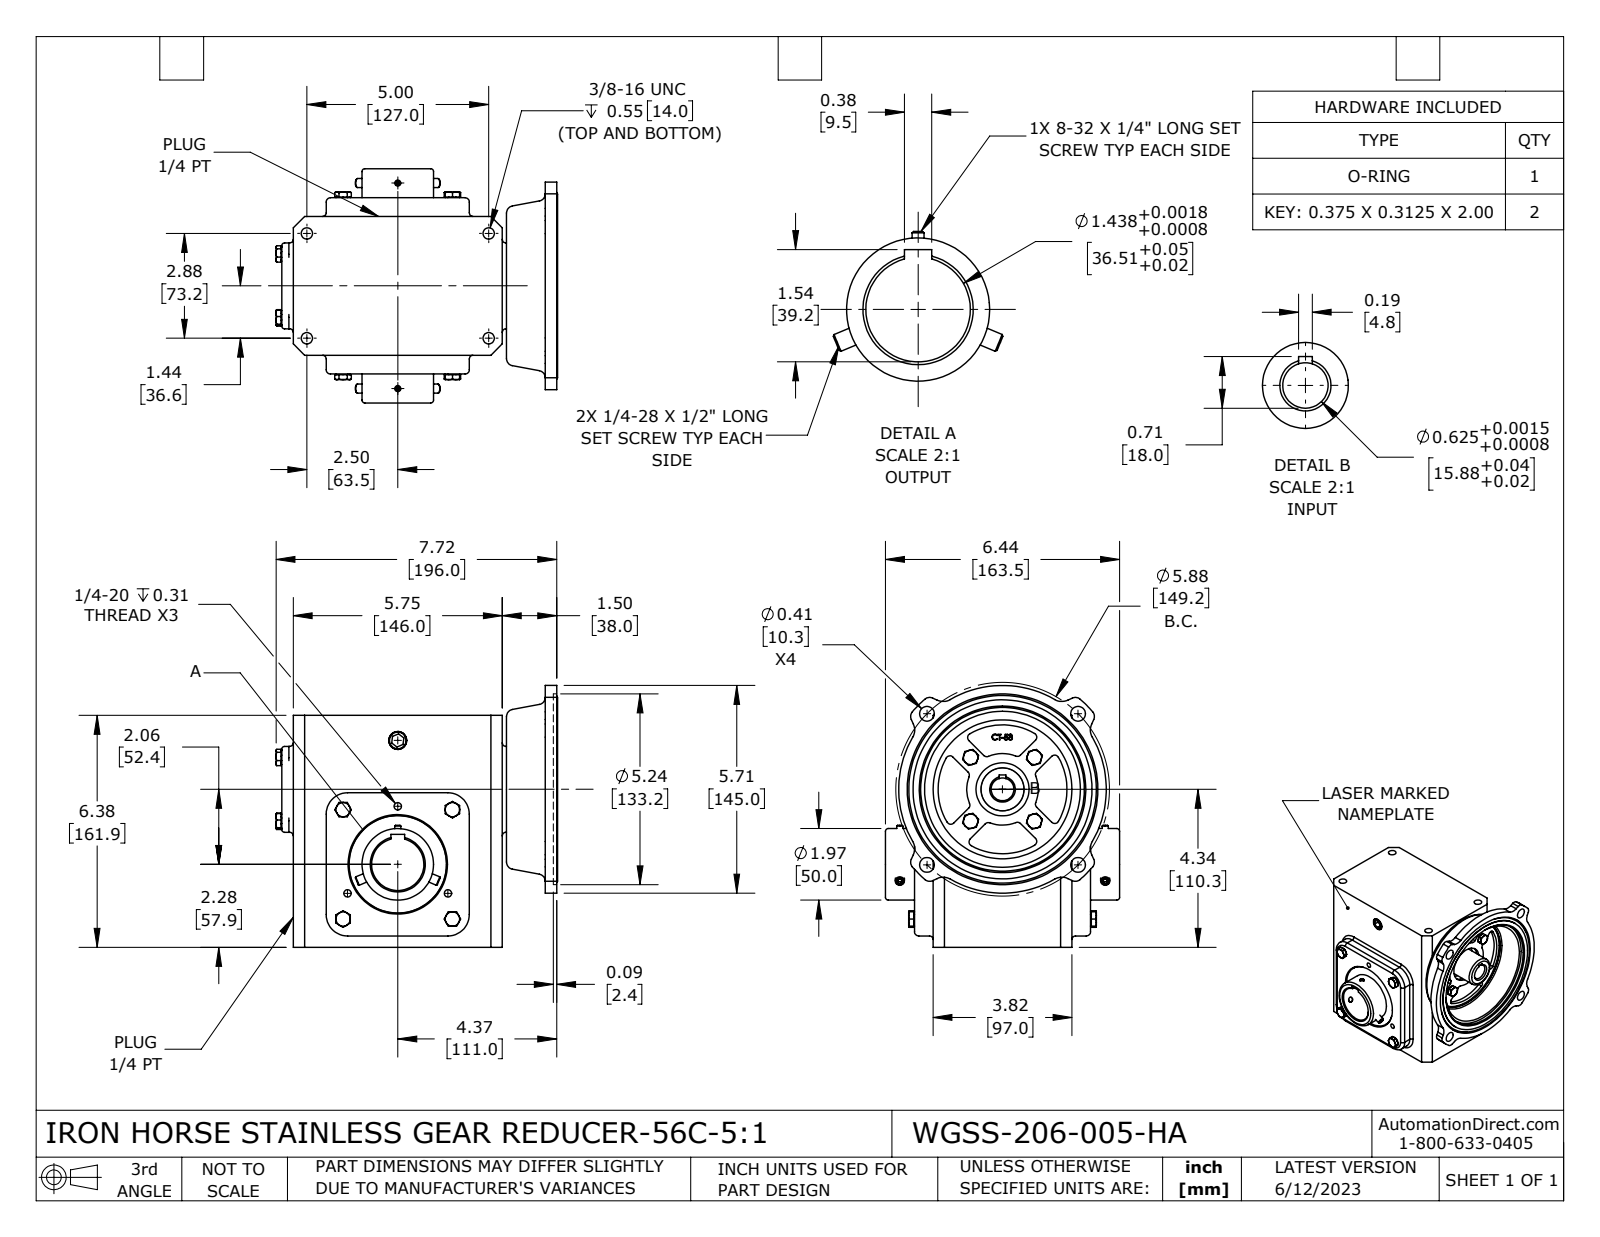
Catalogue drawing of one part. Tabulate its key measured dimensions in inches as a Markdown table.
| quantity | value |
| --- | --- |
| part name | WGSS-206-005-HA |
| STEP written by | SolidWorks 2021 (CONFIG_CONTROL_DESIGN) |
| units | inches |
| bodies | 7 solids, 895 faces (396 planar, 235 cylindrical, 264 other) |
| overall size | 7.74 × 7.197 × 6.437 |
| volume | 159.7 in³ |
| surface area | 323.7 in² |
| round holes (diameter × count) | 0.213 × 4, 0.313 × 4, 0.406 × 4, 0.201 × 3, 0.136 × 2, 0.625 × 1, 0.866 × 1, 1.437 × 1, 1.441 × 1, 1.457 × 1, 1.575 × 1, 3.819 × 1 |
| round bosses / shafts (diameter × count) | 0.394 × 8, 0.25 × 4, 0.164 × 2, 4.921 × 1, 2.677 × 1, 1.969 × 1, 1.181 × 1 |
| partial cylindrical surfaces (radius × count) | 0.118 × 24, 0.098 × 16, 0.394 × 12, 0.197 × 8, 0.079 × 4, 0.315 × 4, 0.591 × 4, 0.984 × 1 |
| main face-to-face distances | 6.375, 3.819, 0.512, 4.331, 5.748, 0.118, 0.315, 7.244, 4.843, 0.157 |
| hole center spacings | 2.858, 2.937, 4.154, 4.944, 1.594, 5.65, 2.762, 2.88 |
